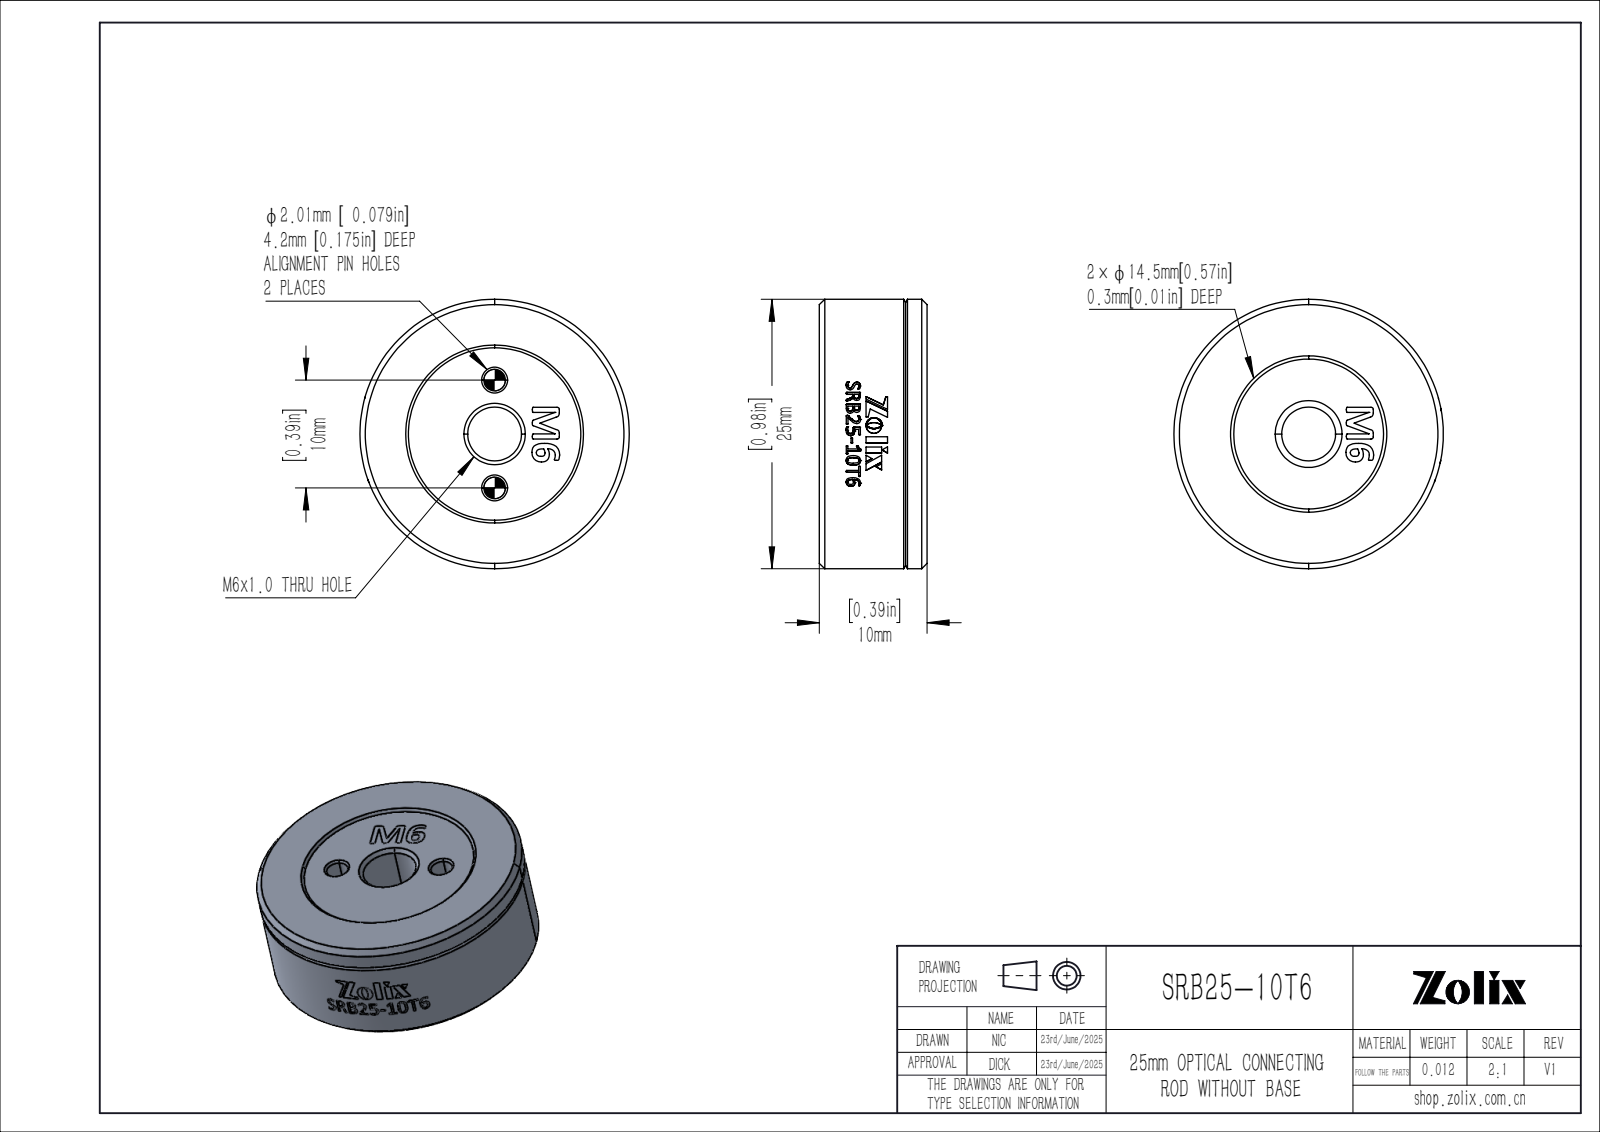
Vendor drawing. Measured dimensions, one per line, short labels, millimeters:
name: SRB25-10T6
written by: SolidWorks 2020 (CONFIG_CONTROL_DESIGN)
unit: mm
bodies: 1 solid, 443 faces (91 planar, 35 cylindrical, 317 other)
size: 25 × 25 × 10
volume: 4 569 mm³; area: 1 915 mm²
holes: 2× ⌀2, 1× ⌀5
bosses: 1× ⌀25
rounds: 1× R12.48
face distances: 10, 9.75, 9.7, 9.45, 0.4, 9.4, 9.3, 9.35, 9.6, 1.99
hole spacings: 5, 10
